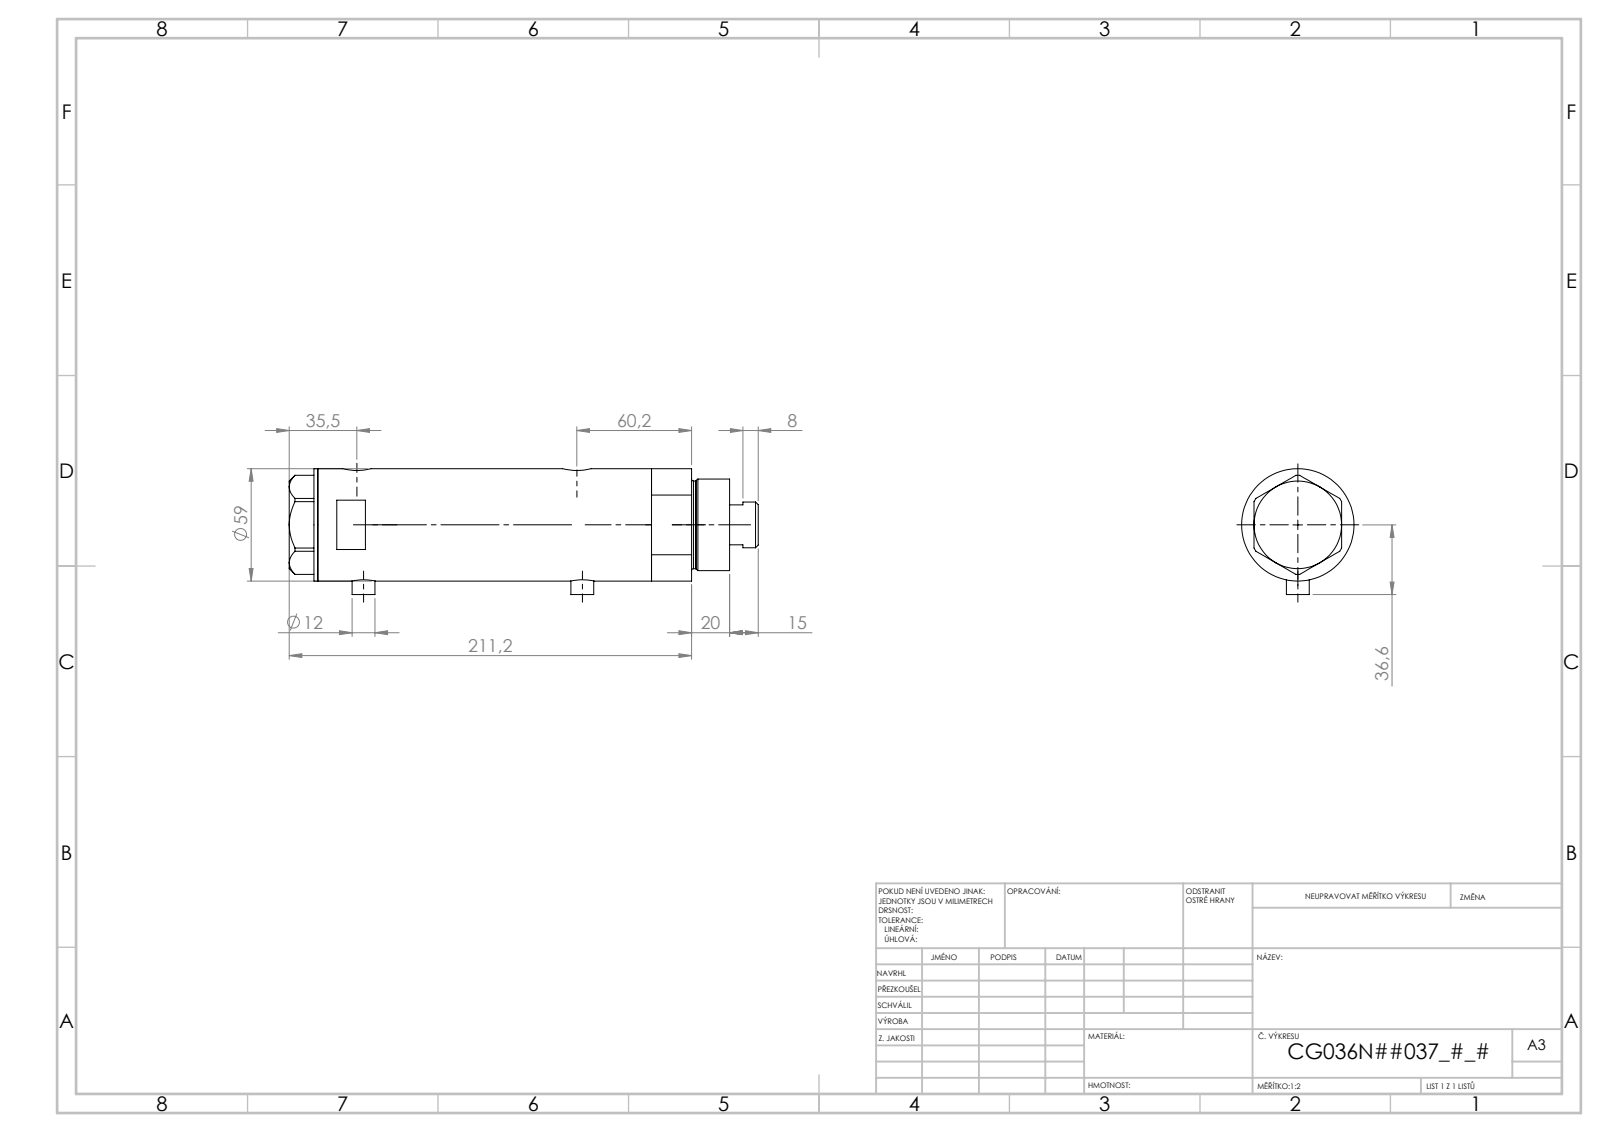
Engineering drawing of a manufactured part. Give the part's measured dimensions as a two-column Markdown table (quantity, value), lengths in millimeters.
| quantity | value |
| --- | --- |
| part name | V270CG_BACK; V270CG_VC; V270CG_FRONT; V270CG_MIDDLE |
| STEP written by | SolidWorks 2019 (CONFIG_CONTROL_DESIGN) |
| units | millimeters |
| bodies | 4 solids, 126 faces (53 planar, 53 cylindrical, 20 other) |
| overall size | 200.42 × 60.1 × 59 |
| volume | 452 799 mm³ |
| surface area | 95 842 mm² |
| round holes (diameter × count) | 5 × 2, 9.73 × 2, 12.5 × 2, 15 × 2, 8.5 × 1, 25 × 1, 26.5 × 1, 36 × 1, 40 × 1, 52 × 1 |
| round bosses / shafts (diameter × count) | 12 × 2, 59 × 1, 48 × 1, 46 × 1, 24 × 1 |
| main face-to-face distances | 94.34, 23.5, 70.84, 15, 38.5, 109.34, 185.42, 170.42, 146.92, 76.08 |
| hole center spacings | 2.9, 3.5, 69.15, 72.05, 72.65, 75.55, 2.89, 2.91 |
